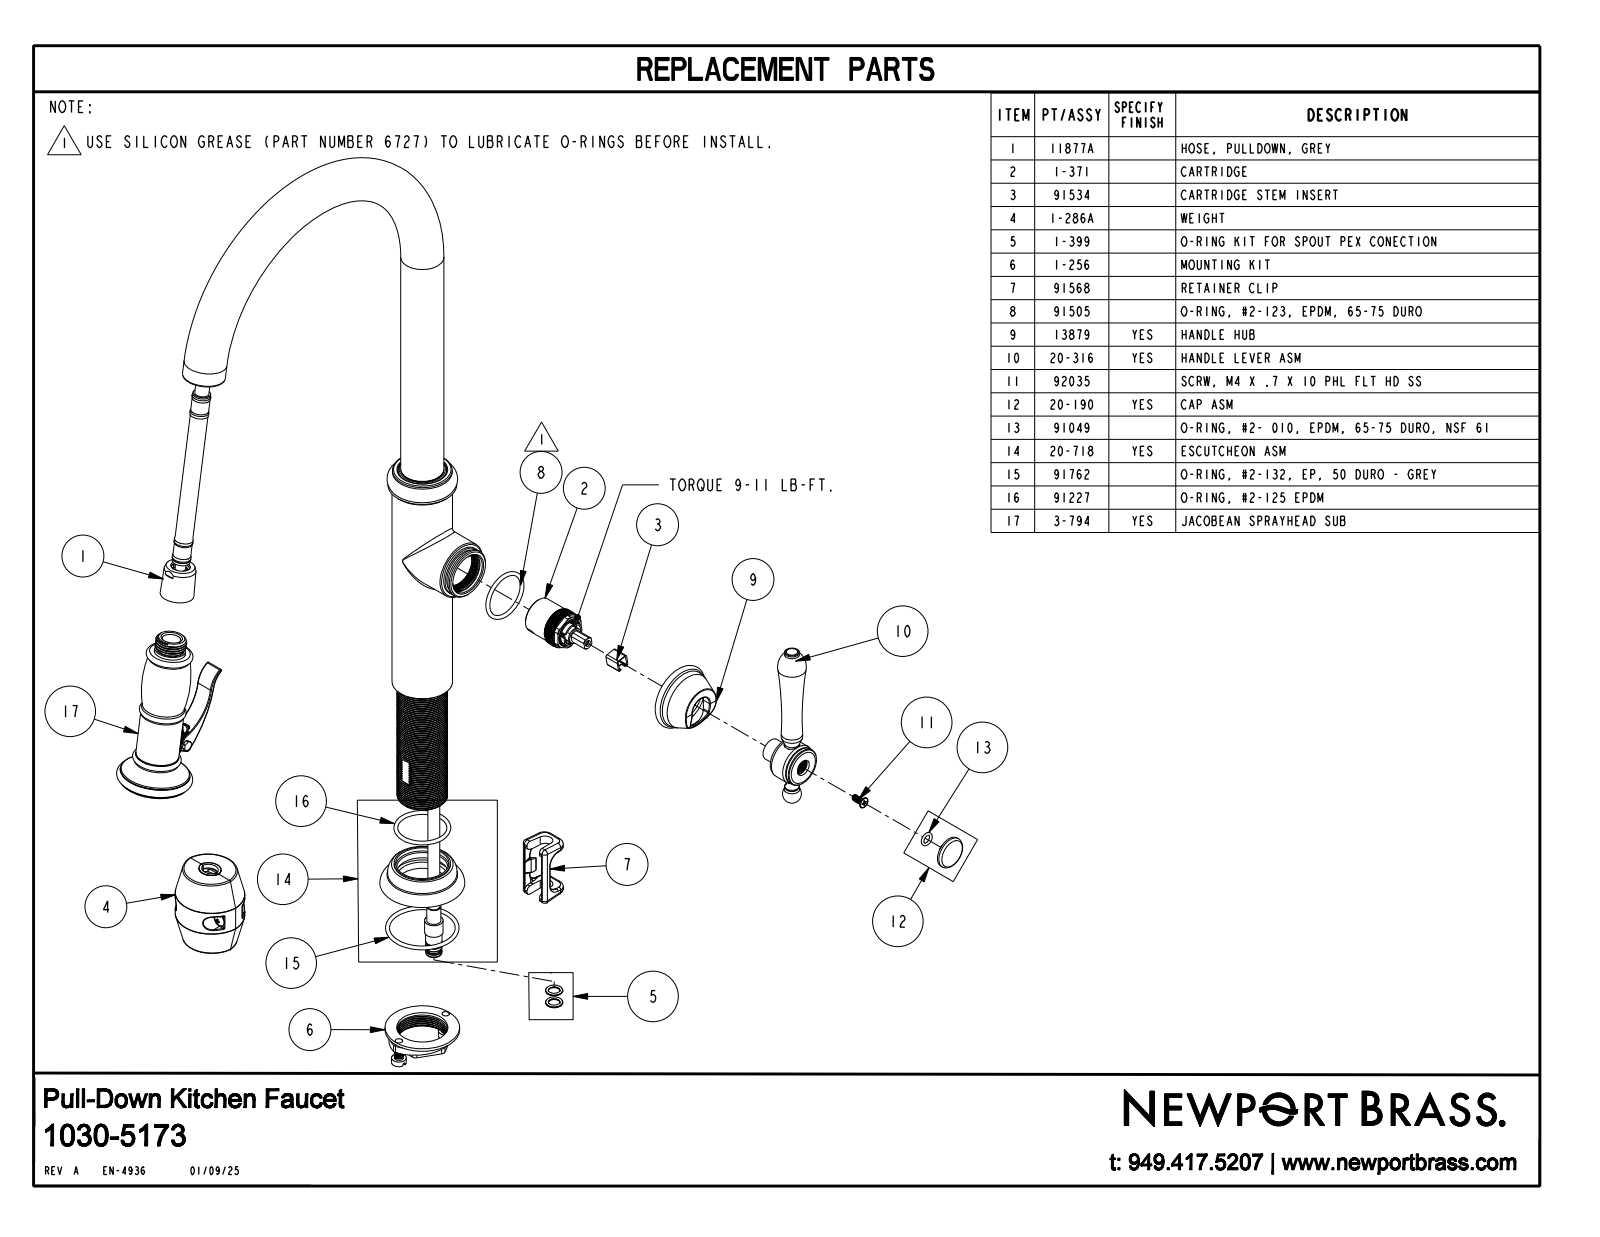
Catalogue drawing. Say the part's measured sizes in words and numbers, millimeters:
The part is named "JACOBEAN25". Its 3-D file was written by "CREO PARAMETRIC BY PTC INC, 2023134 (CONFIG_CONTROL_DESIGN)". It is 2 solids with 2305 faces: 1352 planar, 460 cylindrical and 493 other. Overall it measures 482.4 by 275.8 by 115.5 millimeters. Its volume is 729 700 cubic millimeters and its surface area 111 100 square millimeters. Round holes: 18 of diameter 1, 1 of diameter 4.3, 1 of diameter 5.3, 1 of diameter 12, 1 of diameter 34.3, 1 of diameter 35.8, 1 of diameter 39.4, 1 of diameter 41.9, 1 of diameter 50.5. Round bosses or shafts: 18 of diameter 2.6, 1 of diameter 44.5, 1 of diameter 40.6, 1 of diameter 40, 1 of diameter 38.4, 1 of diameter 32.5, 1 of diameter 29, 1 of diameter 29. Partial cylindrical surfaces (rounded edges, fillets, slot ends): 21 of radius 0.8, 18 of radius 0.5, 14 of radius 1.7, 7 of radius 0.6, 5 of radius 1.5, 4 of radius 1.1, 2 of radius 8.3, 1 of radius 1. The main face-to-face distances are 15.5, 175.8, 160.3, 189.7, 174.2, 14, 2.2, 13.3, 173.6, 187.6. The hole center spacings are 9.3, 16.2, 17.6, 12, 3.3, 6.4, 14.3, 18.4.
